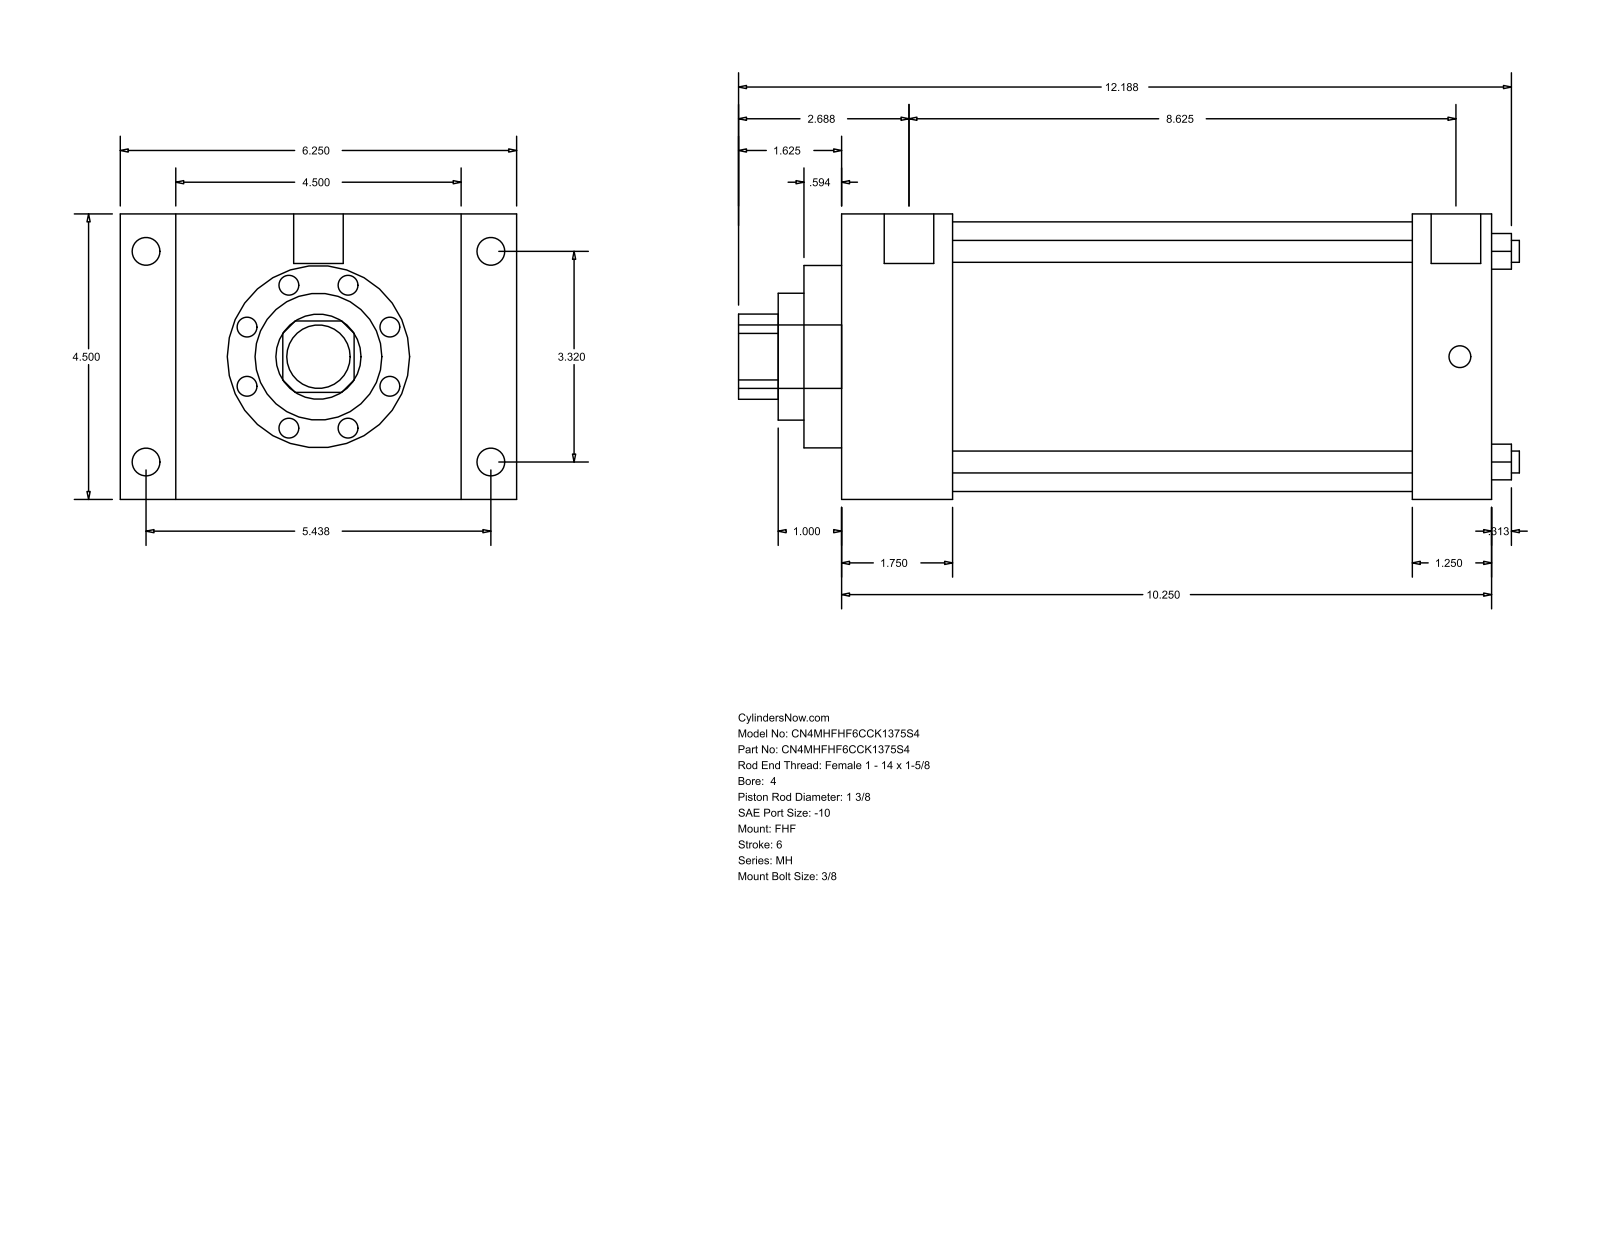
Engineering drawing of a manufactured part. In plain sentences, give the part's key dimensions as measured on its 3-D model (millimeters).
The part is named "MH_FHF__0400_1.375". Its 3-D file was written by "GSSL Pune (CONFIG_CONTROL_DESIGN)". It is 0 solids with 90 faces: 61 planar, 29 cylindrical and 0 other. Overall it measures 312.74 by 158.75 by 114.3 millimeters. Round holes: 4 of diameter 8.76, 1 of diameter 34.92, 1 of diameter 50.8, 1 of diameter 73.03, 1 of diameter 107.95. Round bosses or shafts: 4 of diameter 11.13, 4 of diameter 8.73, 2 of diameter 19.84, 1 of diameter 25.4. Partial cylindrical surfaces (rounded edges, fillets, slot ends): 1 of radius 17.06. The main face-to-face distances are 114.3, 260.35, 44.45, 215.9, 22.23, 136.53, 158.76, 228.61, 184.16, 31.74. The hole center spacings are 59.62, 84.32, 119.25.
